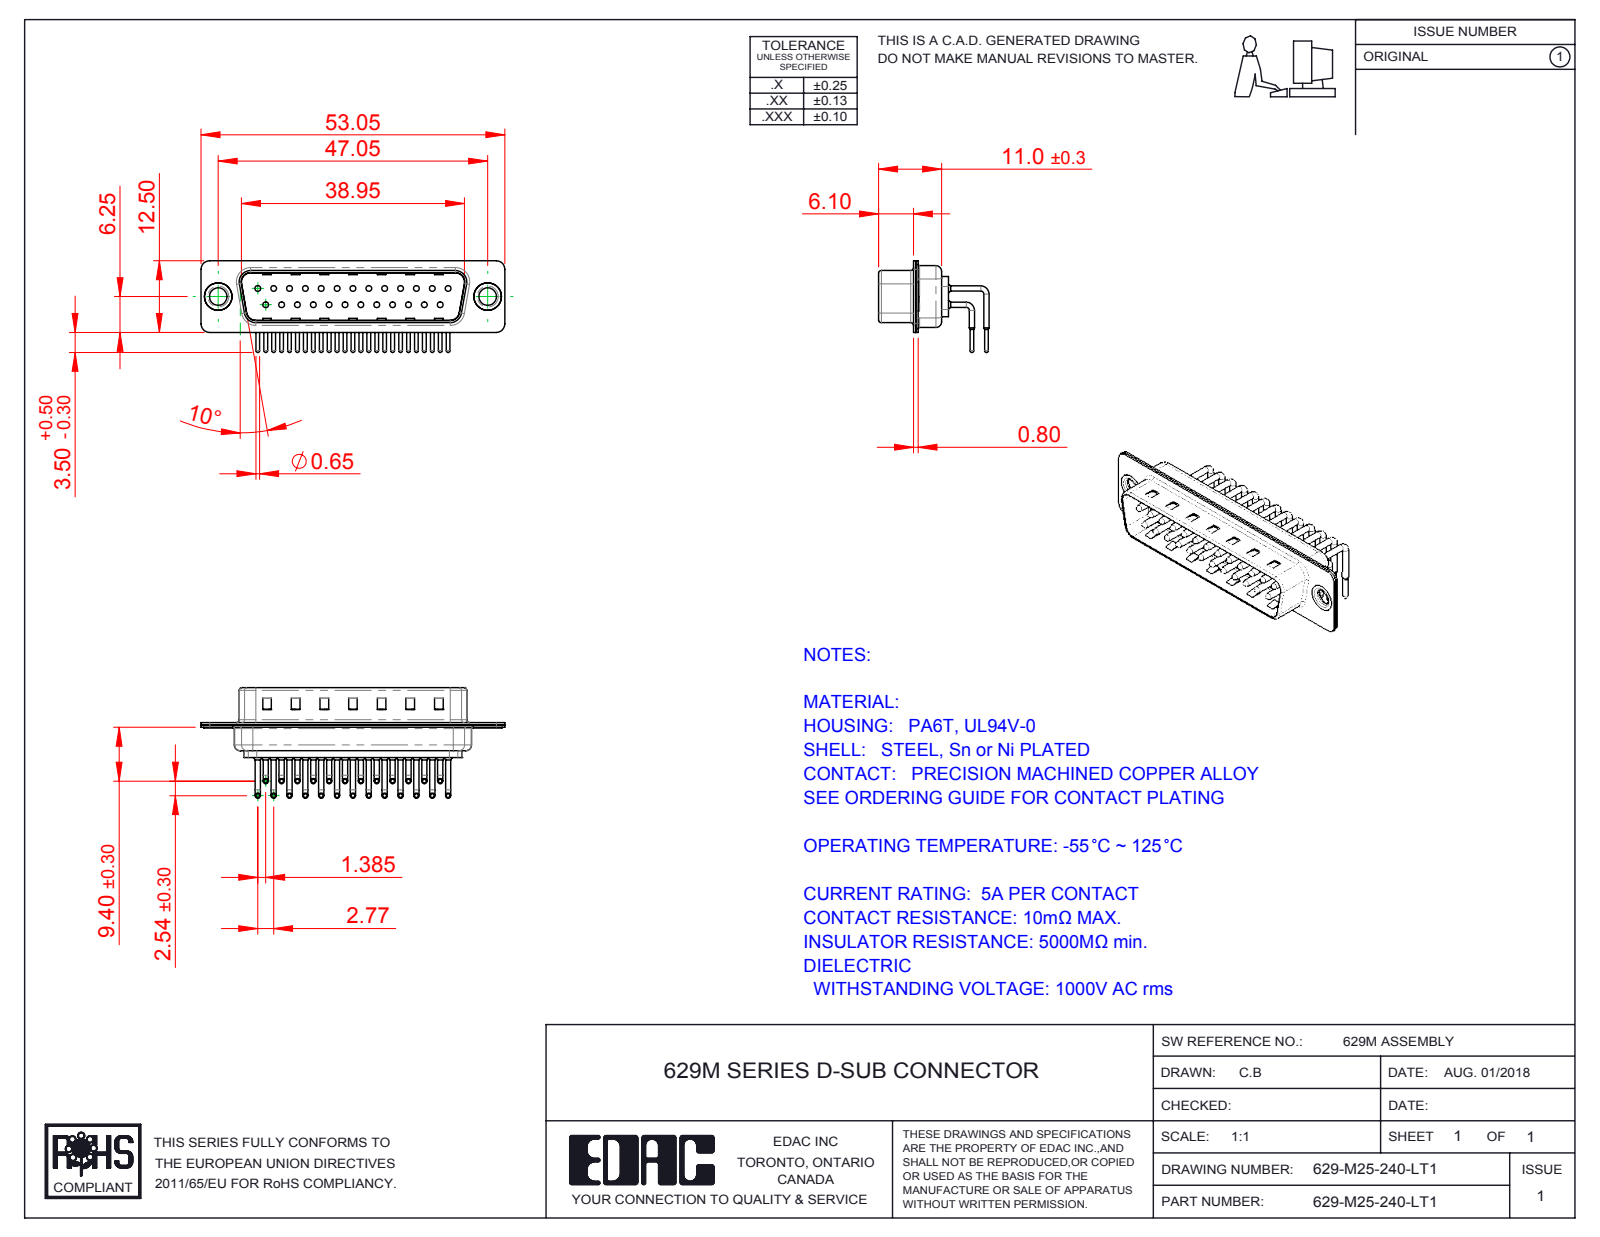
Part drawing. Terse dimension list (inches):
name: 629M Shell Front_25 Contacts; 629M Contact Row 1; 629M Shell Rear_25 Contacts; 629M Contact Row 2 (+3 more)
written by: SolidWorks 2016 (CONFIG_CONTROL_DESIGN)
unit: in
bodies: 30 solids, 3100 faces (1771 planar, 1021 cylindrical, 308 other)
size: 2.089 × 0.759 × 0.63
volume: 0.173 in³; area: 11.8 in²
holes: 25× ⌀0.039, 25× ⌀0.067, 25× ⌀0.079, 2× ⌀0.12, 2× ⌀0.157, 2× ⌀0.189
bosses: 50× ⌀0.035, 25× ⌀0.059, 25× ⌀0.026, 2× ⌀0.197, 2× ⌀0.193, 2× ⌀0.14
rounds: 25× R0.04, 16× R0.059, 12× R0.079, 8× R0.02, 8× R0.063, 4× R0.01, 4× R0.024, 4× R0.026
face distances: 0.016, 0.033, 0.376, 0.343, 0.049, 0.409, 0.059, 0.075, 0.014, 0.24
hole spacings: 0.124, 0.109, 0.218, 0.327, 0.436, 0.545, 0.198, 0.295
